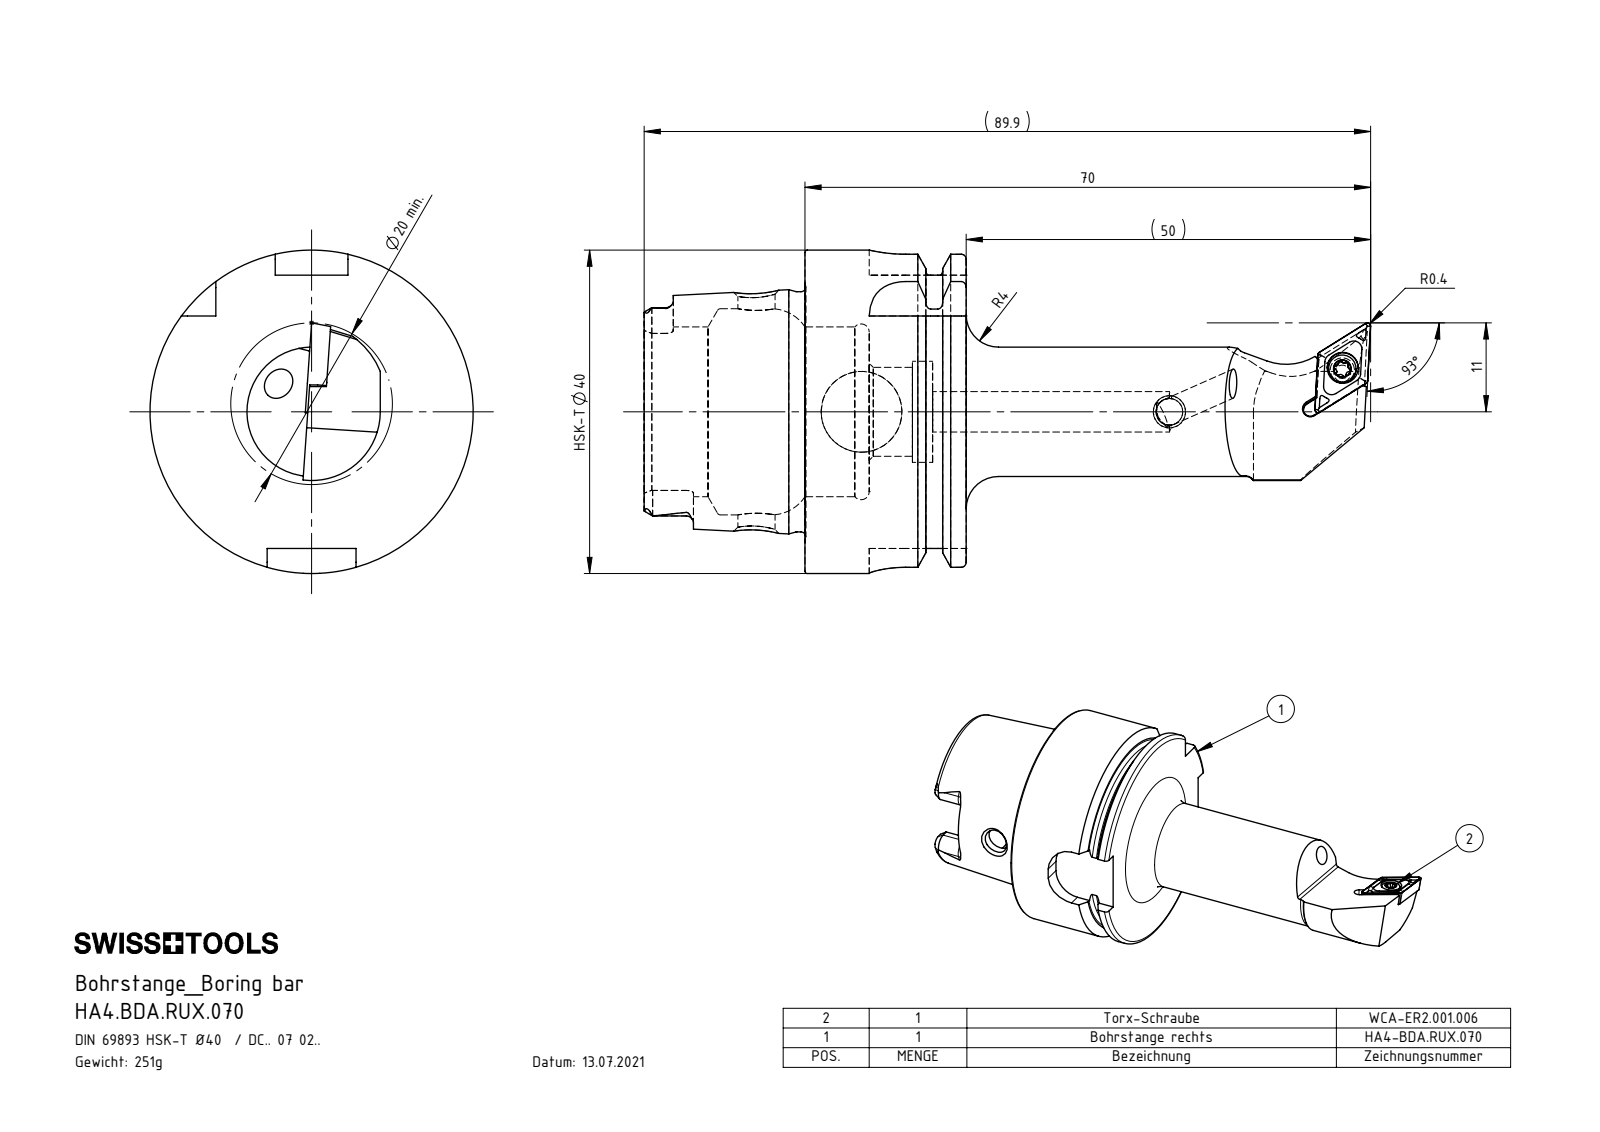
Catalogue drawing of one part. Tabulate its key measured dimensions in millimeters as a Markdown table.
| quantity | value |
| --- | --- |
| part name | DCMT070204; KVT_MB_600_040; HA4.BDA.RUX.070; WCA-ER2.001.006_A (+1 more) |
| STEP written by | SolidWorks 2017 (AUTOMOTIVE_DESIGN) |
| units | millimeters |
| bodies | 5 solids, 238 faces (82 planar, 62 cylindrical, 94 other) |
| overall size | 89.9 × 40 × 40 |
| volume | 31 947 mm³ |
| surface area | 12 800 mm² |
| round holes (diameter × count) | 3.3 × 2, 2.05 × 1, 2.8 × 1, 3 × 1, 3.85 × 1, 4.6 × 1, 5 × 1, 10 × 1, 11 × 1, 12.5 × 1, 21 × 1, 25.5 × 1 |
| round bosses / shafts (diameter × count) | 40 × 1, 34.75 × 1, 29.71 × 1, 16 × 1, 4 × 1, 3.4 × 1, 2.5 × 1 |
| partial cylindrical surfaces (radius × count) | 0.21 × 6, 0.9 × 6, 1.88 × 4, 4.5 × 4, 0.36 × 3, 0.36 × 3, 0.5 × 1, 0.85 × 1 |
| main face-to-face distances | 19.95, 7.95, 12, 19.9, 27.85, 39.85, 35.7, 15.8, 7.85, 4.15 |
| hole center spacings | 38.1 |
